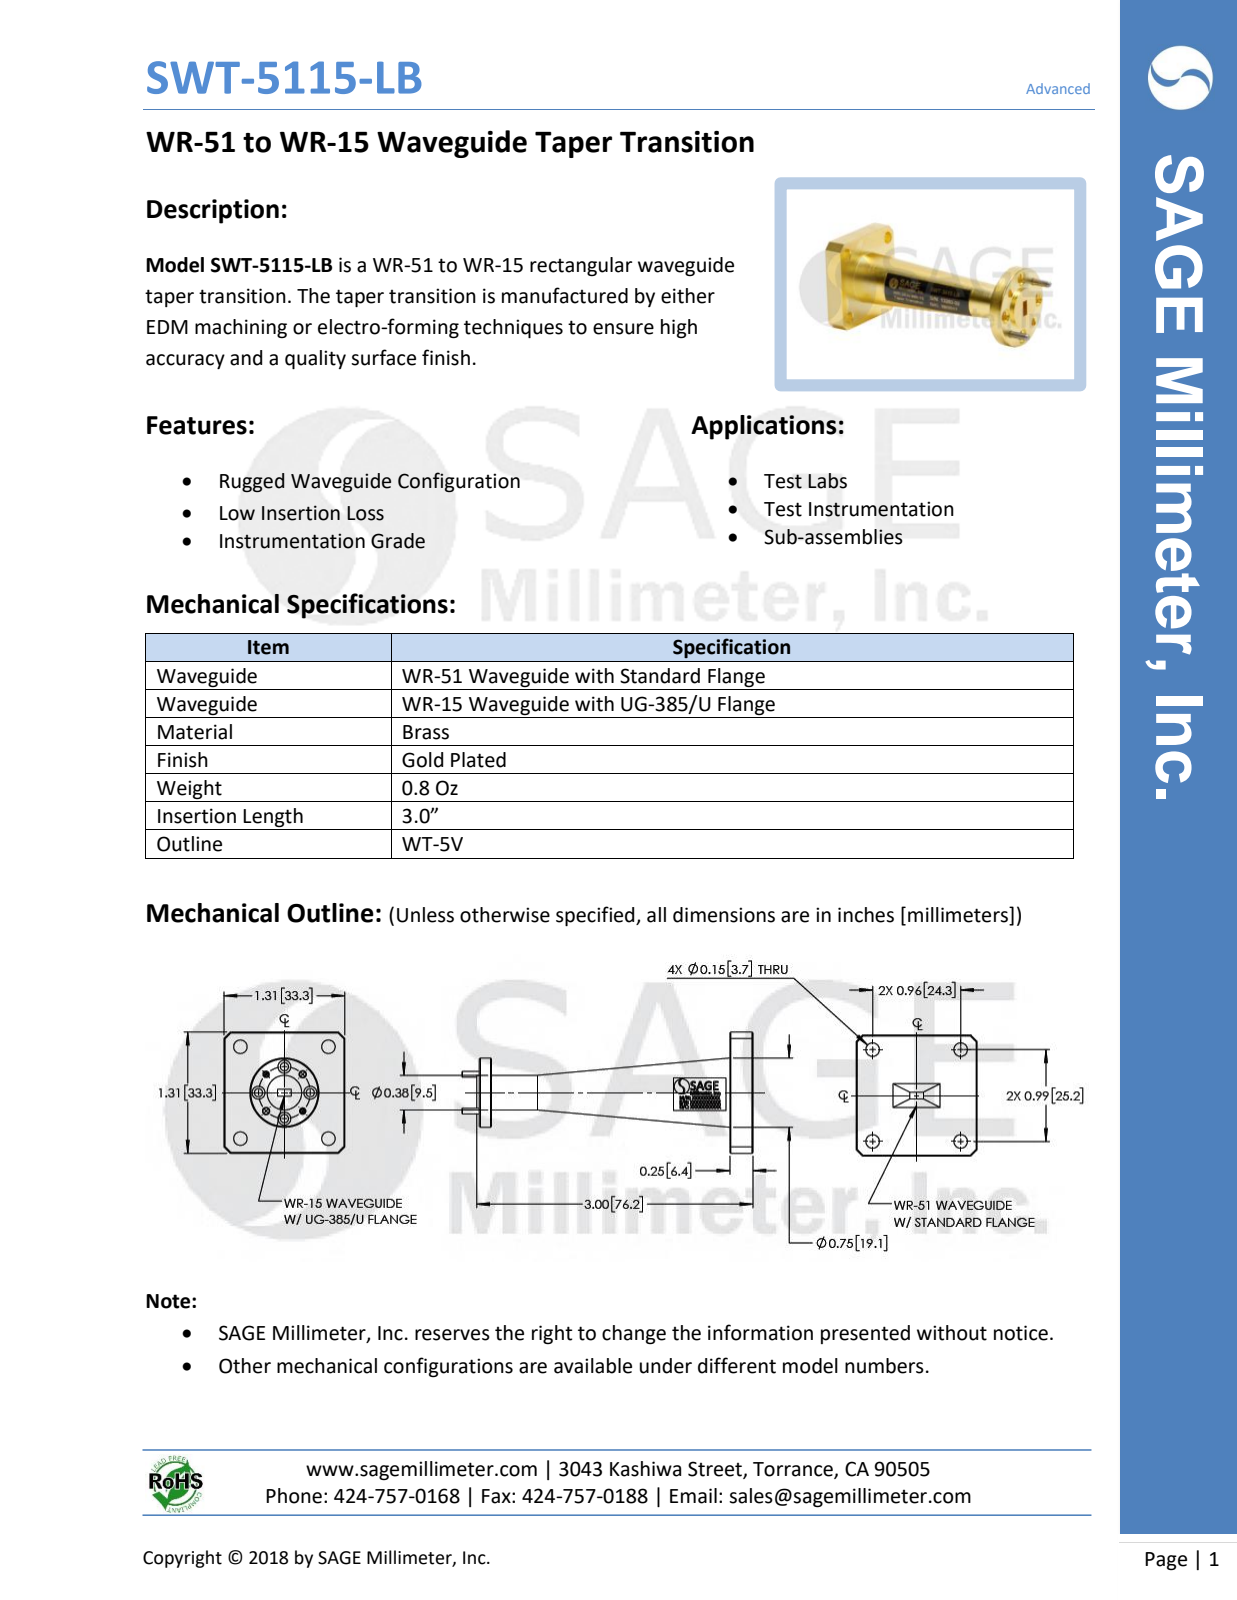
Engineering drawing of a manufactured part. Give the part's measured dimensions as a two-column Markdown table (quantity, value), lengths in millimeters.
| quantity | value |
| --- | --- |
| part name | SWT-5115-LB |
| STEP written by | SolidWorks 2016 (CONFIG_CONTROL_DESIGN) |
| units | millimeters |
| bodies | 3 solids, 111 faces (47 planar, 42 cylindrical, 22 other) |
| overall size | 80.3 × 33.3 × 33.3 |
| volume | 17 370 mm³ |
| surface area | 6 606 mm² |
| round holes (diameter × count) | 2.3 × 4, 3.6 × 4, 3.7 × 4, 1.5 × 2, 1.7 × 2 |
| round bosses / shafts (diameter × count) | 1.6 × 2, 19.1 × 1, 9.5 × 1 |
| main face-to-face distances | 6.4, 33.3, 72.1, 65.8, 75.4, 69.1, 3.3, 6.1, 71.9, 75.2 |
| hole center spacings | 5.5, 10.1, 13.2, 10.4, 13.3, 13.6, 14.3, 18.8 |
